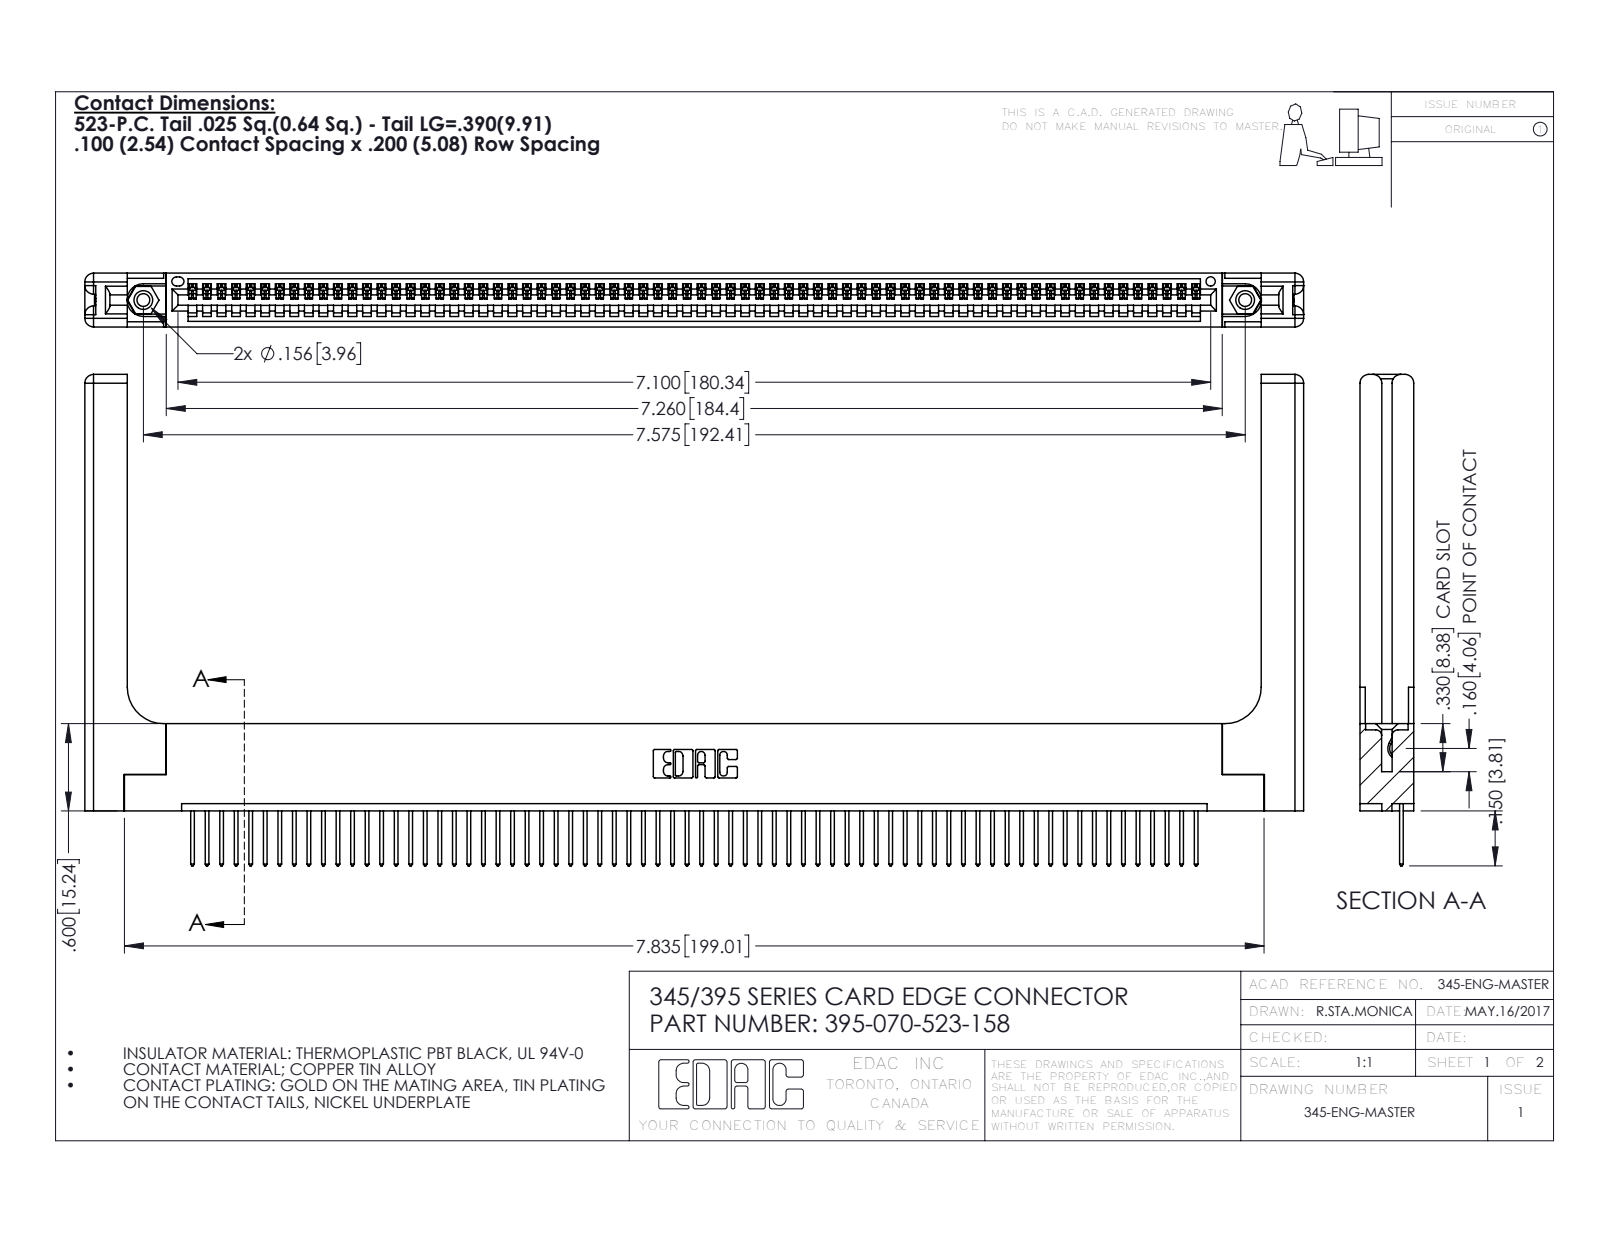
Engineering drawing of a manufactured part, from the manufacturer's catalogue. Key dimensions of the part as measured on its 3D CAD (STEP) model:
Part name (STEP PRODUCT): 345-220-058_345-220-058; 345 Part_Flush Mounting Lugs - 0.156 Dia-TH; 345-292-001_345-293-123; 395-070-523-158 (+1 more)
STEP written by: SolidWorks 2016 (CONFIG_CONTROL_DESIGN)
Units: inches
Bodies: 75 solids, 4442 faces (3028 planar, 1354 cylindrical, 60 other)
Overall size (bounding box): 8.379 × 3.377 × 0.37
Volume: 1.765 in³ · Surface area: 50.99 in²
Round holes (diameter × count): ⌀0.089 ×2, ⌀0.125 ×2, ⌀0.156 ×2, ⌀0.064 ×1
Round bosses / shafts (diameter × count): ⌀0.155 ×2
Partial cylindrical surfaces — rounded edges, fillets, slot ends (radius × count): R0.006 ×140, R0.01 ×140, R0.01 ×22, R0.06 ×16, R0.007 ×6, R0.031 ×6, R0.026 ×3, R0.03 ×2
Main face-to-face distances: 0.072, 0.298, 0.37, 0.2, 0.098, 0.272, 0.025, 0.225, 0.148, 0.15
Hole centre spacings: 0.27, 7.339, 7.575
